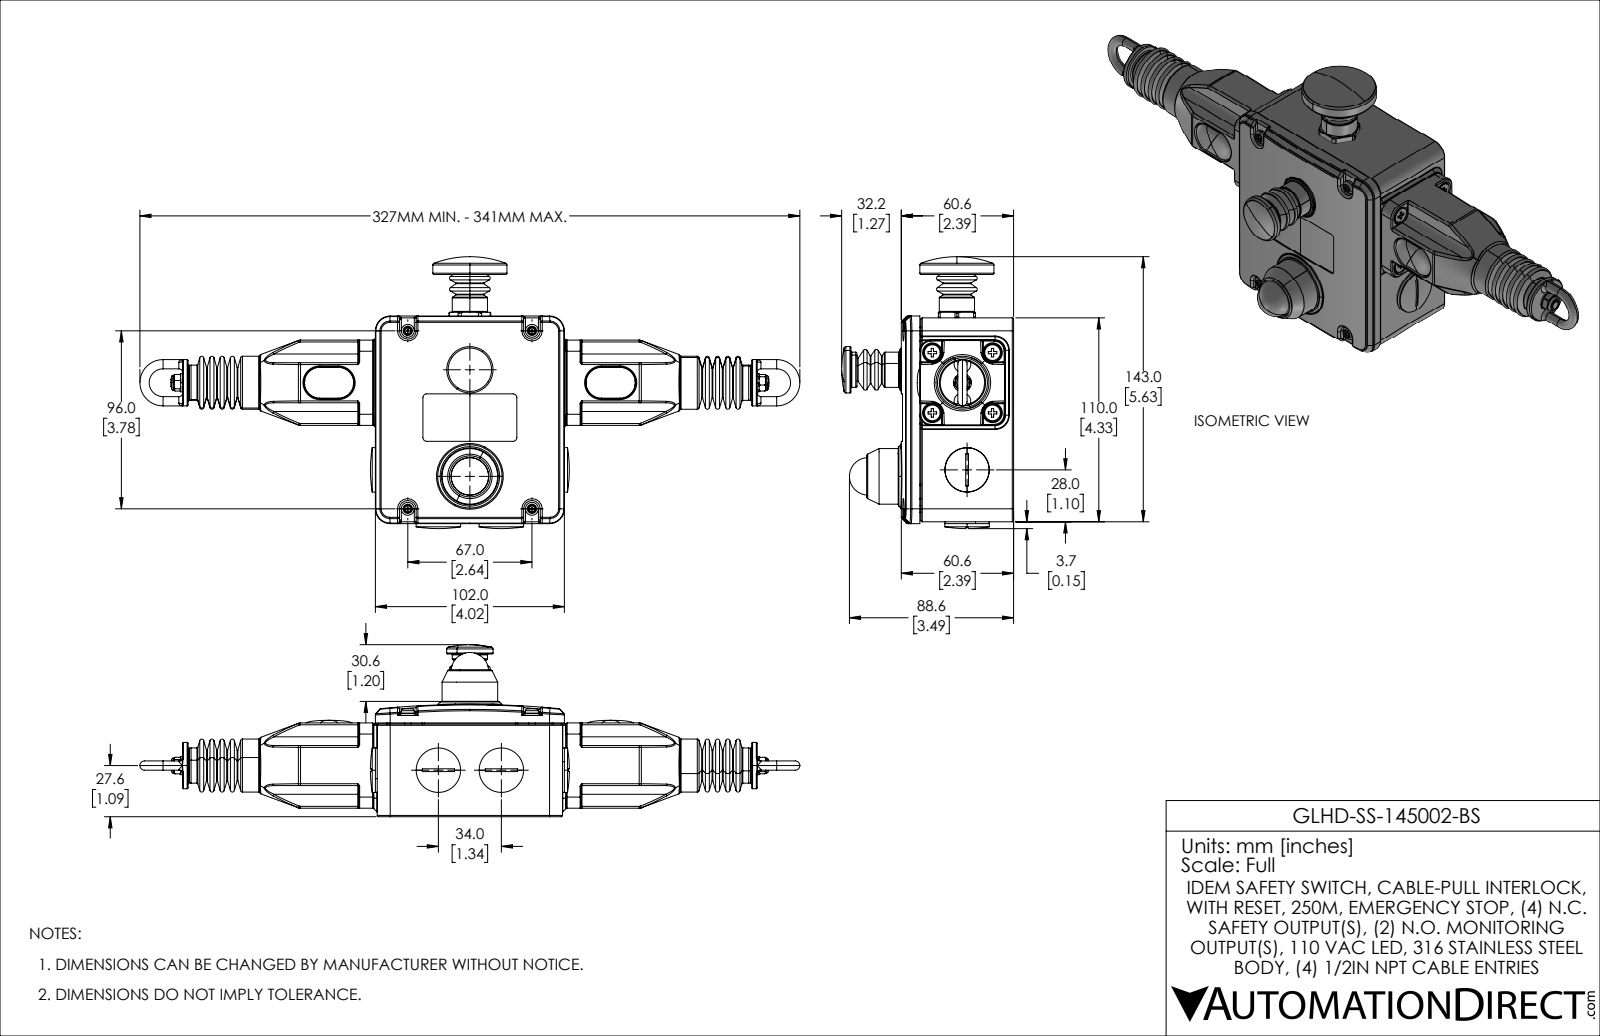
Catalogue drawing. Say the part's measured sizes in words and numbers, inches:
The part is named "GLHD-SS-145002-AS". Its 3-D file was written by "SolidWorks 2021 (AUTOMOTIVE_DESIGN)". It is 54 solids with 5065 faces: 1385 planar, 1706 cylindrical and 1974 other. Overall it measures 14.024 by 5.775 by 3.654 inches. Its volume is 22.29 cubic inches and its surface area 357.4 square inches. Round holes: 9 of diameter 0.197, 7 of diameter 0.161, 6 of diameter 0.354, 5 of diameter 0.209, 4 of diameter 0.094, 4 of diameter 0.13, 4 of diameter 0.157, 4 of diameter 0.189, 4 of diameter 0.213, 4 of diameter 0.228, 4 of diameter 0.378, 3 of diameter 0.067. Round bosses or shafts: 7 of diameter 0.197, 5 of diameter 0.276, 4 of diameter 0.787, 4 of diameter 0.335, 4 of diameter 0.173, 4 of diameter 0.138, 4 of diameter 0.051, 3 of diameter 0.945. Partial cylindrical surfaces (rounded edges, fillets, slot ends): 267 of radius 0.02, 140 of radius 0.039, 76 of radius 0.008, 56 of radius 0.028, 24 of radius 0.012, 18 of radius 0.079, 14 of radius 0.004, 14 of radius 0.006. The main face-to-face distances are 0.039, 0.138, 0.079, 2.067, 2.181, 0.114, 0.157, 4.016, 0.48, 0.217. The hole center spacings are 1.28, 0.905, 0.374, 0.228, 0.902, 0.907, 1.339, 1.809.
